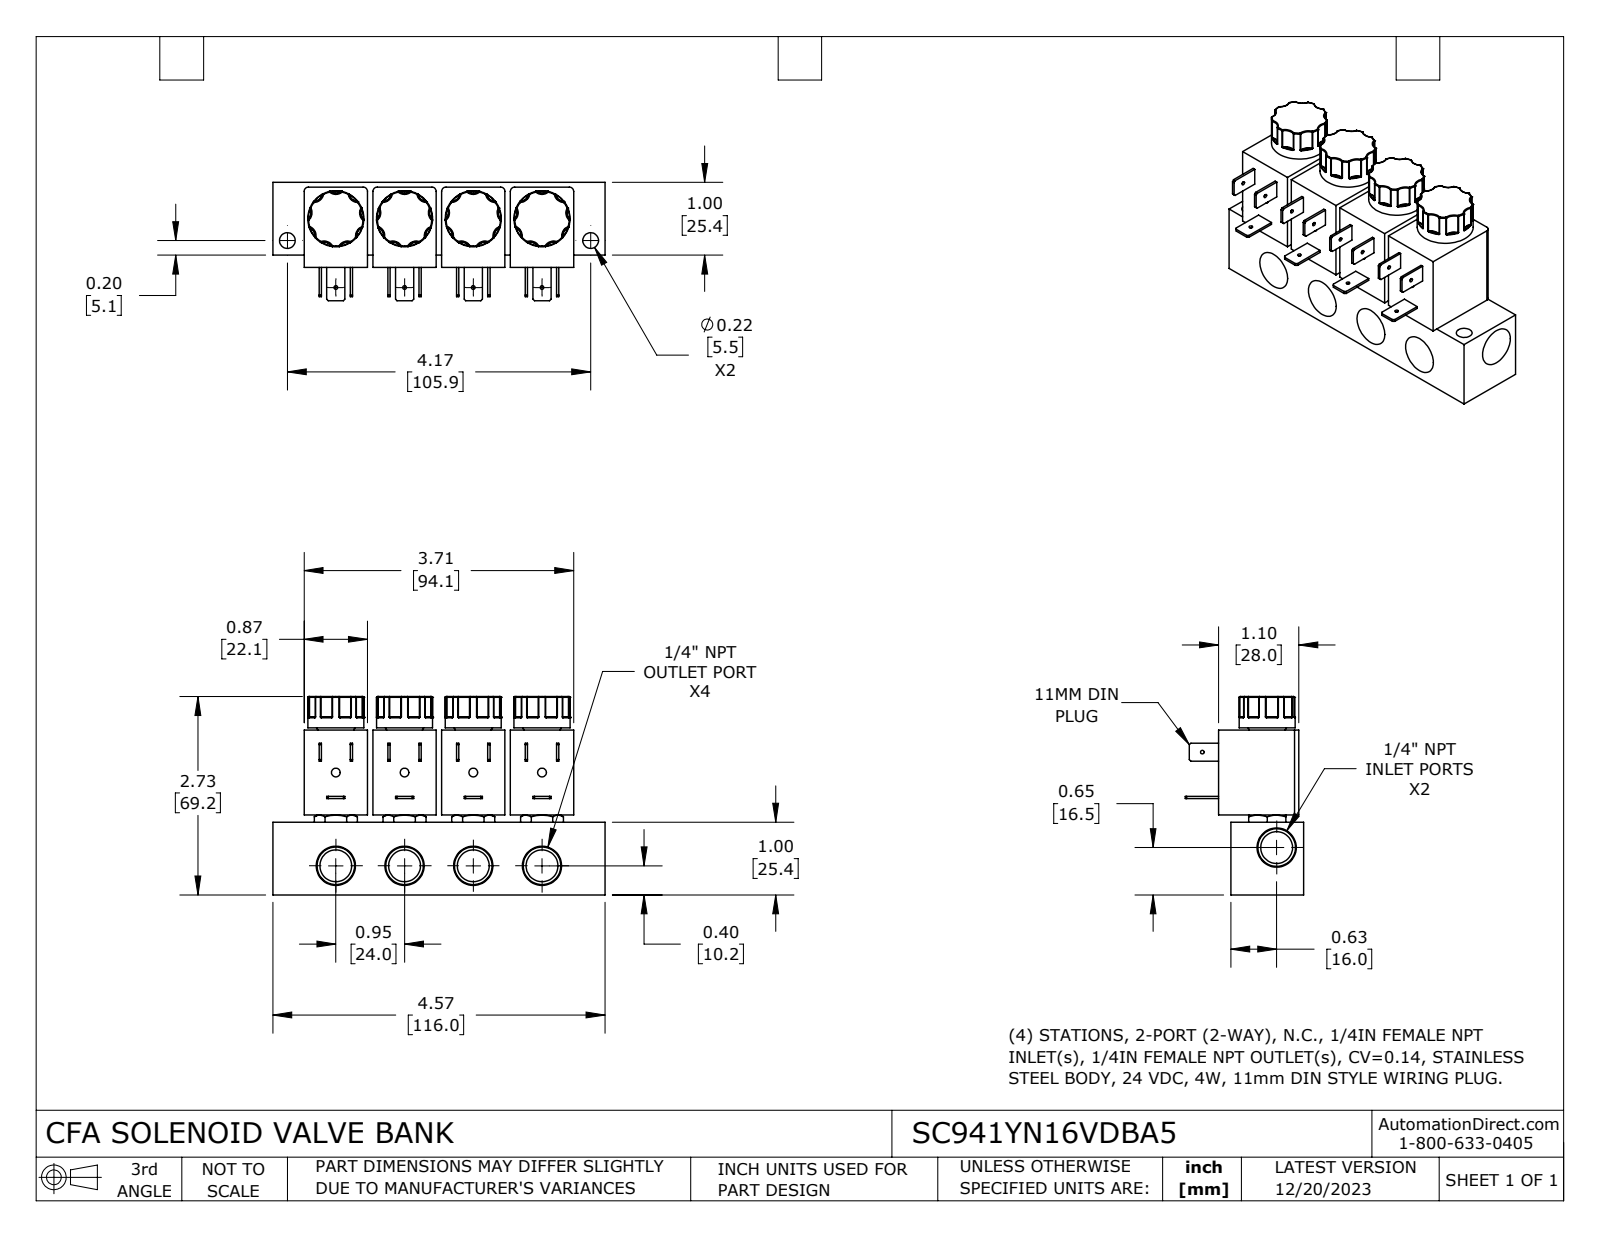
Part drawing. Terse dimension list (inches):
name: SC941YN16VDBA5
written by: SolidWorks 2023 (CONFIG_CONTROL_DESIGN)
unit: in
bodies: 1 solid, 868 faces (192 planar, 184 cylindrical, 492 other)
size: 4.567 × 2.725 × 1.627
volume: 9.182 in³; area: 61.05 in²
holes: 5× ⌀0.05, 5× ⌀0.438, 4× ⌀0.12, 2× ⌀0.217
bosses: 4× ⌀0.77
rounds: 72× R0.01, 34× R0.133, 8× R0.06, 2× R0.132
face distances: 1, 0.945, 1.169, 1.89, 1.815, 0.87, 0.169, 0.065, 0.935, 1.104
hole spacings: 0.945, 1.282, 1.593, 0.945, 1.89, 1.89, 2.835, 1.593
